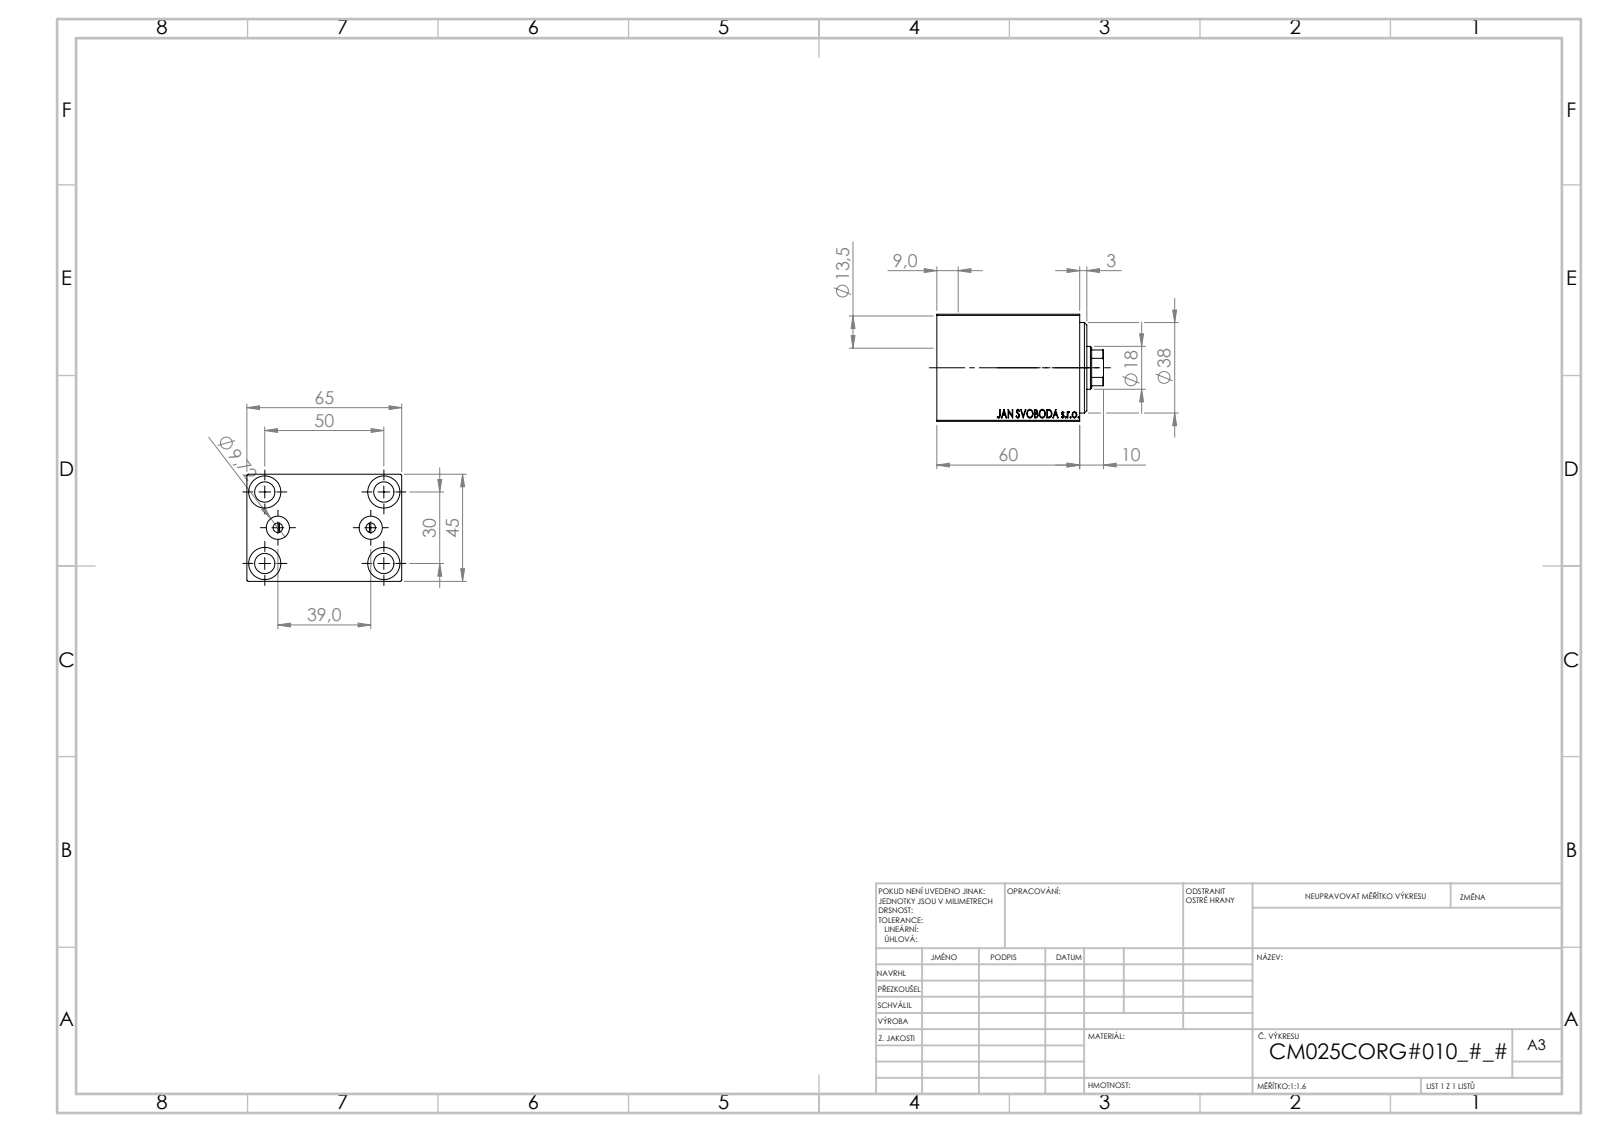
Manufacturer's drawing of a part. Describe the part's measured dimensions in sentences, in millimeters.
The part is named "V450CM_VC_B; V450CM_C_Body; V450CM_C_VCP". Its 3-D file was written by "SolidWorks 2019 (CONFIG_CONTROL_DESIGN)". It is 3 solids with 858 faces: 408 planar, 56 cylindrical and 394 other. Overall it measures 71 by 65 by 45 millimeters. Its volume is 154 631 cubic millimeters and its surface area 38 558 square millimeters. Round holes: 5 of diameter 8.5, 4 of diameter 13.5, 2 of diameter 4, 2 of diameter 9.72, 1 of diameter 18, 1 of diameter 21.5, 1 of diameter 25, 1 of diameter 27, 1 of diameter 38. Partial cylindrical surfaces (rounded edges, fillets, slot ends): 1 of radius 8.5. The main face-to-face distances are 45, 65, 27.5, 5, 55, 60, 32.5, 8, 10, 9. The hole center spacings are 15.98, 29.15, 46.96, 19.5, 30, 50, 58.31, 39.
